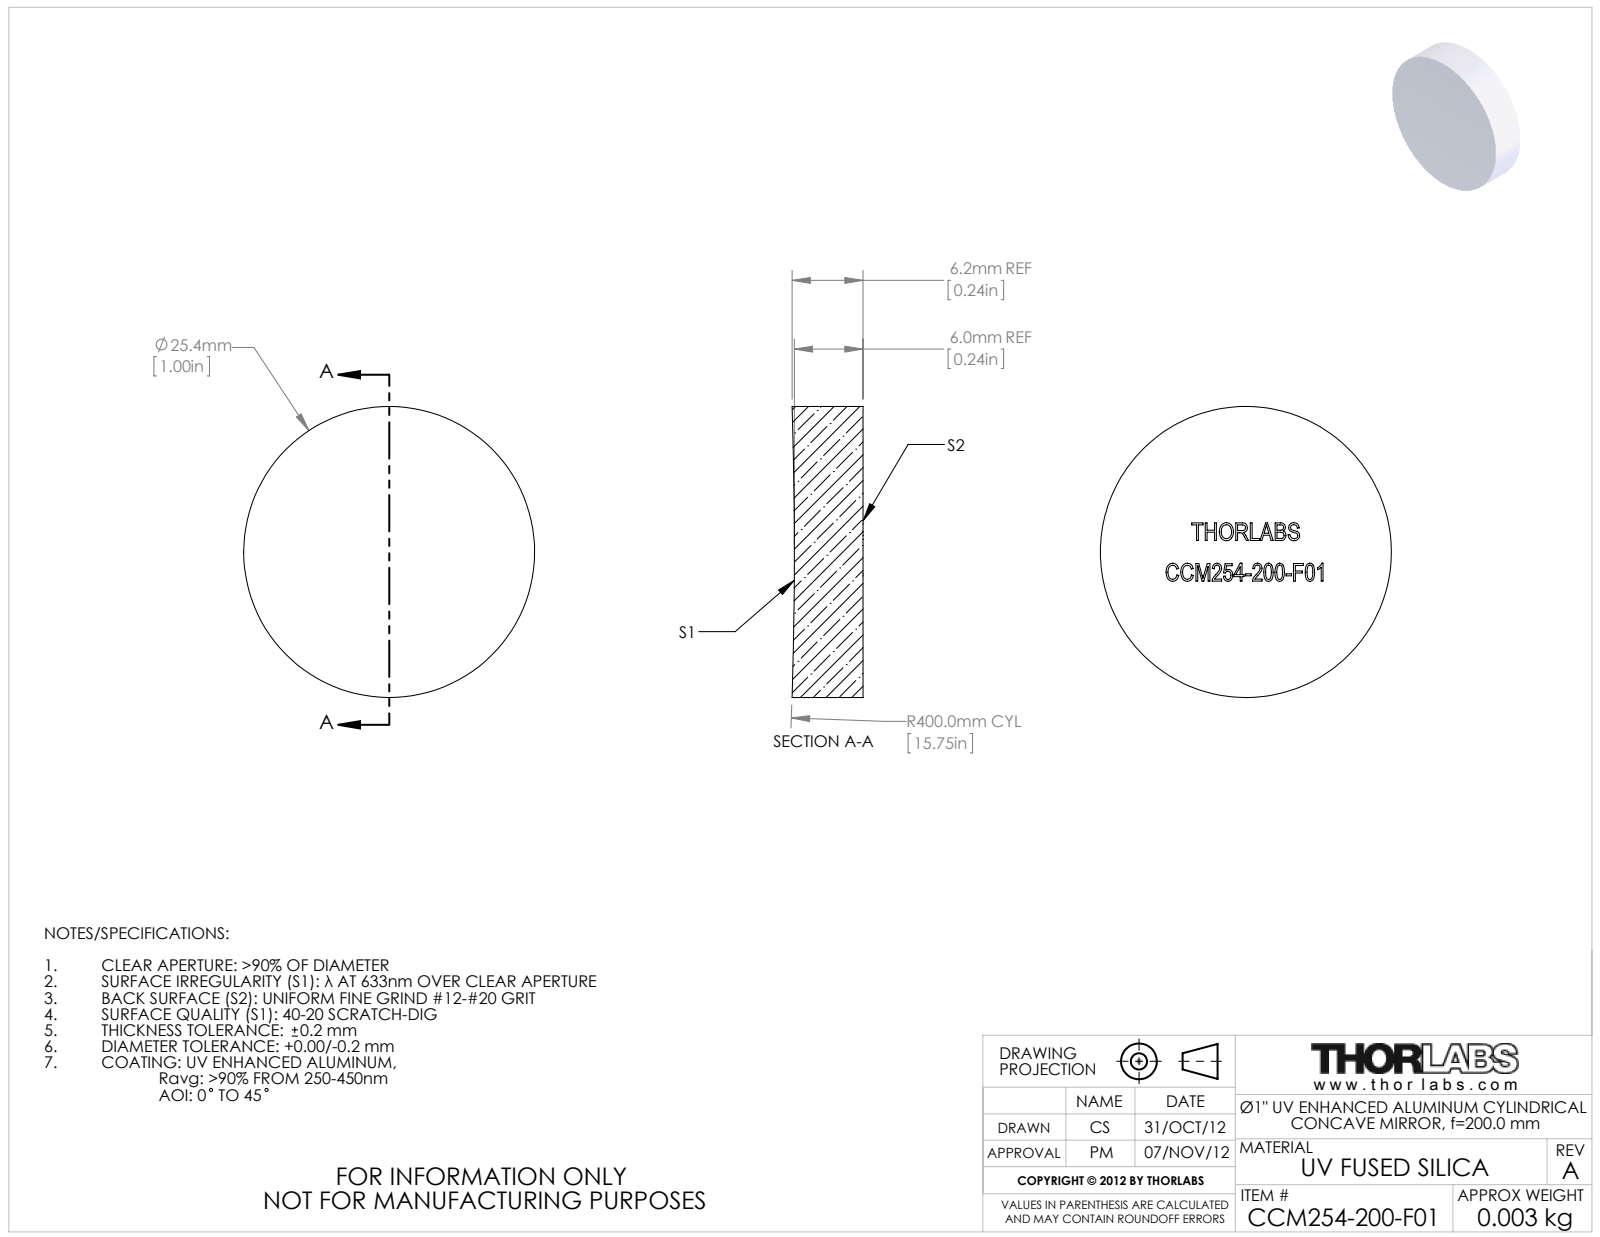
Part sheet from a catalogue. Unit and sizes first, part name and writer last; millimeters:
Units: millimetres
Overall size (bounding box): 25.4 × 25.4 × 6.2
Round bosses / shafts (diameter × count): ⌀25.4 ×1
Partial cylindrical surfaces — rounded edges, fillets, slot ends (radius × count): R400 ×1
Volume: 3 066 mm³ · Surface area: 1 500 mm²
Bodies: 1 solid, 36 faces (32 planar, 4 cylindrical, 0 other)
Part name (STEP PRODUCT): TTN005969-E0W
STEP written by: SolidWorks 2012 (CONFIG_CONTROL_DESIGN)
